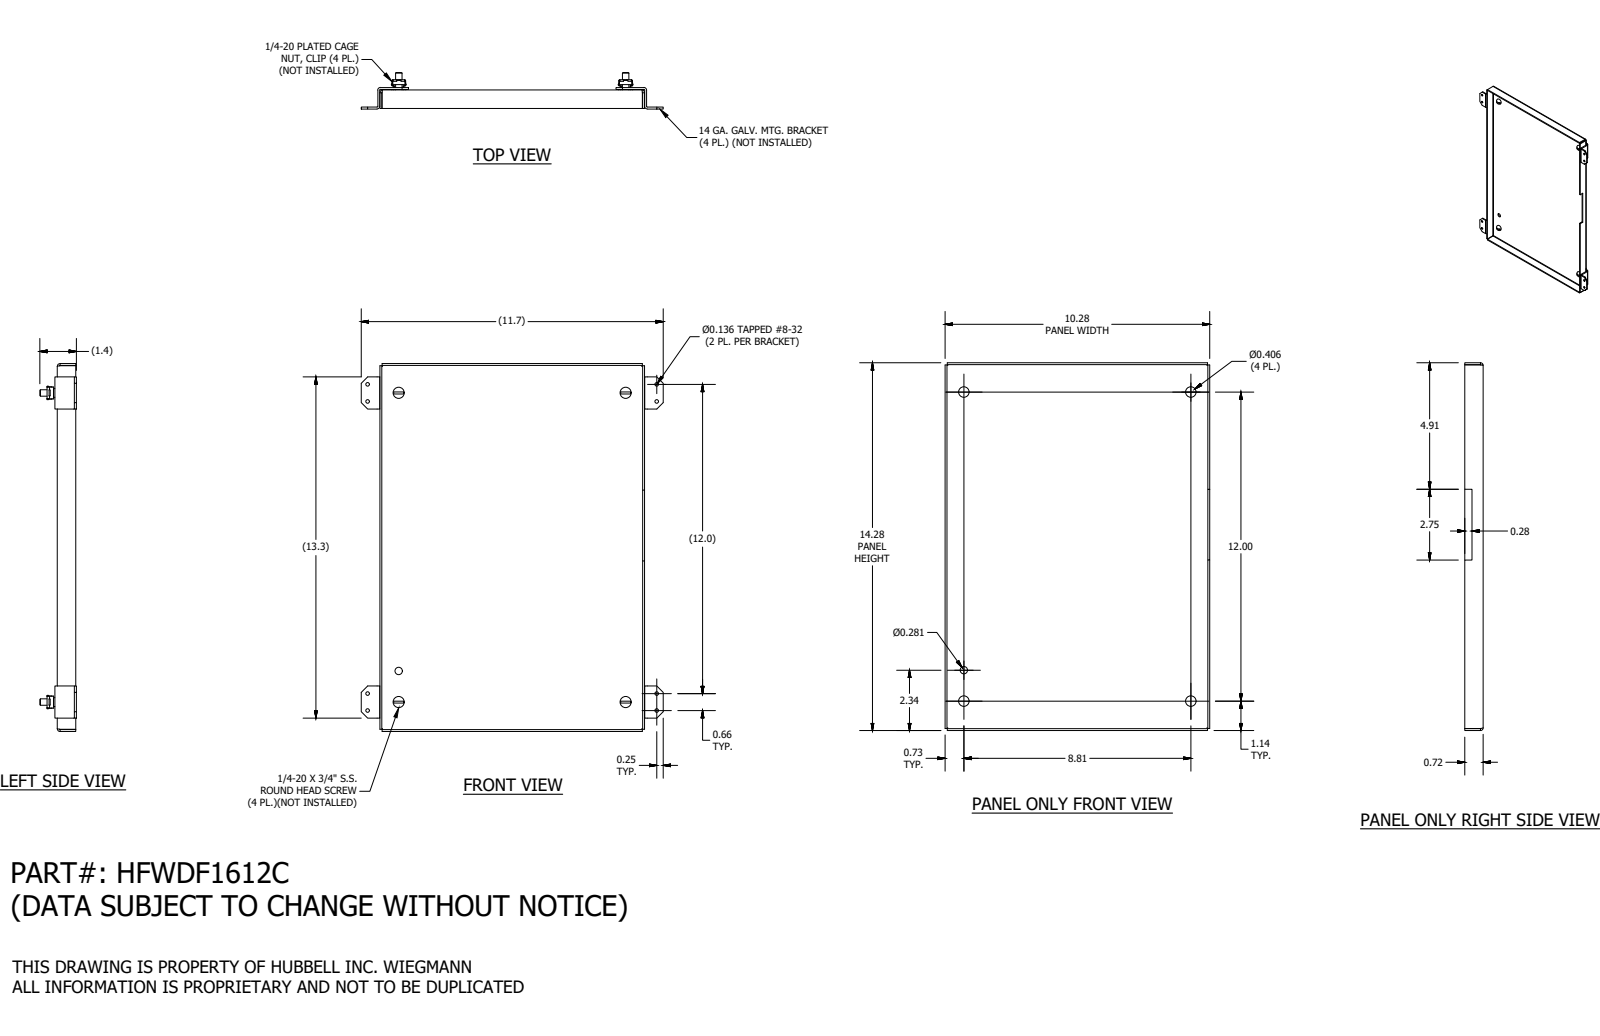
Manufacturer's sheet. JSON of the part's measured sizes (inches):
{"part_name": "HFWDF1612C", "step_written_by": "SolidWorks 2023 (AUTOMOTIVE_DESIGN)", "units": "inches", "bodies": {"solids": 13, "faces": 595, "planar": 418, "cylindrical": 161, "other": 16}, "overall_size": [14.281, 11.726, 1.415], "volume_in3": 14.21, "surface_area_in2": 392.5, "round_holes": [[0.136, 8], [0.185, 4], [0.328, 4], [0.406, 4], [0.281, 1]], "round_bosses_or_shafts": [[0.25, 4]], "partial_cylinders_radius": [[0.025, 20], [0.021, 16], [0.045, 12], [0.031, 8], [0.105, 8], [0.021, 4]], "face_to_face_distances": [0.074, 10.207, 14.207, 0.094, 10.281, 10.133, 0.078, 10.285, 14.133, 14.281], "hole_center_spacings": [1.251, 10.025, 12, 0.66, 11.227, 11.246, 11.732, 12.389]}
